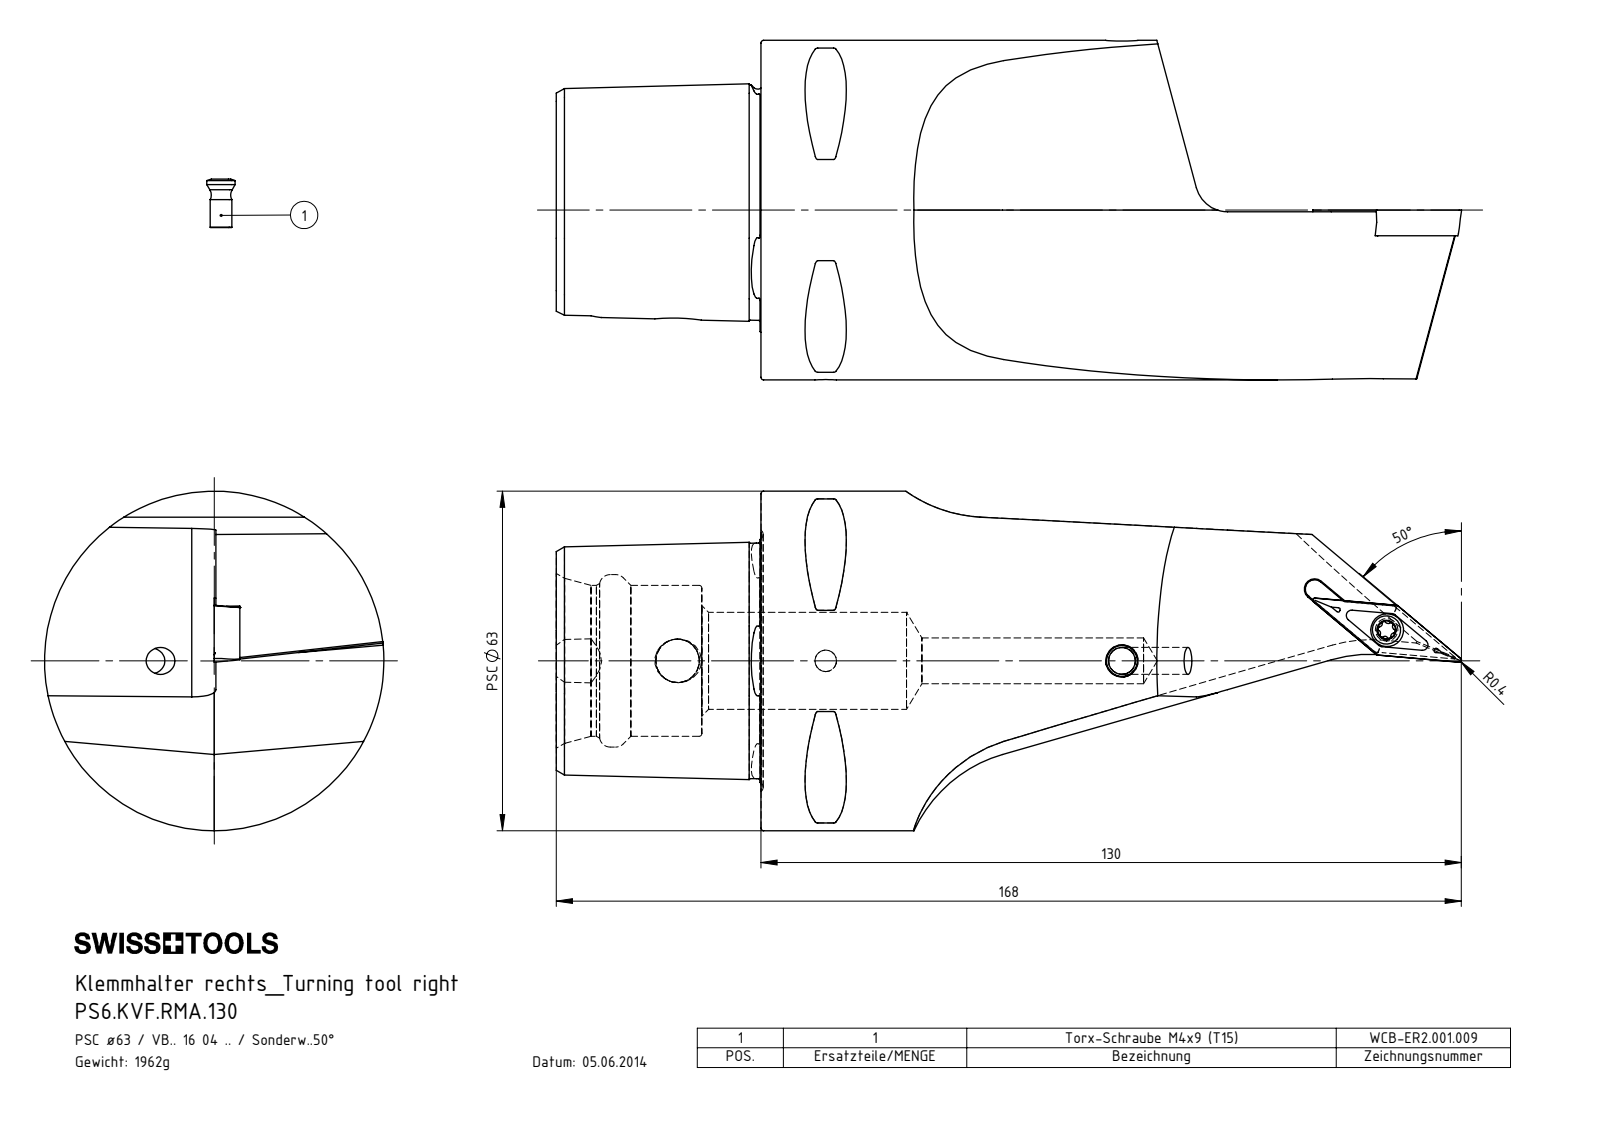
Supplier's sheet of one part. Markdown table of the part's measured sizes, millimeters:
| quantity | value |
| --- | --- |
| part name | PS6-KVF.RMA.130; KVT_MB_600_060; WCB-ER2.001.009_A; VBMT160404 (+1 more) |
| STEP written by | SolidWorks 2012 (CONFIG_CONTROL_DESIGN) |
| units | millimeters |
| bodies | 5 solids, 272 faces (55 planar, 70 cylindrical, 147 other) |
| overall size | 168.04 × 63 × 63 |
| volume | 249 473 mm³ |
| surface area | 36 459 mm² |
| round holes (diameter × count) | 5 × 2, 3.3 × 1, 4 × 1, 4.4 × 1, 6.1 × 1, 8.1 × 1, 8.5 × 1, 18 × 1, 28 × 1, 32 × 1 |
| round bosses / shafts (diameter × count) | 63 × 1, 6 × 1, 5.25 × 1, 4 × 1 |
| partial cylindrical surfaces (radius × count) | 0.5 × 8, 0.34 × 6, 0.59 × 6, 26 × 4, 6 × 2, 1.75 × 1 |
| main face-to-face distances | 38, 24.88, 4.46, 27, 11, 55.8, 37.8, 10.8, 4.76, 28.96 |
| hole center spacings | 27.5, 49.46, 49.56, 55, 82.5, 104.28, 104.39, 131.75 |
